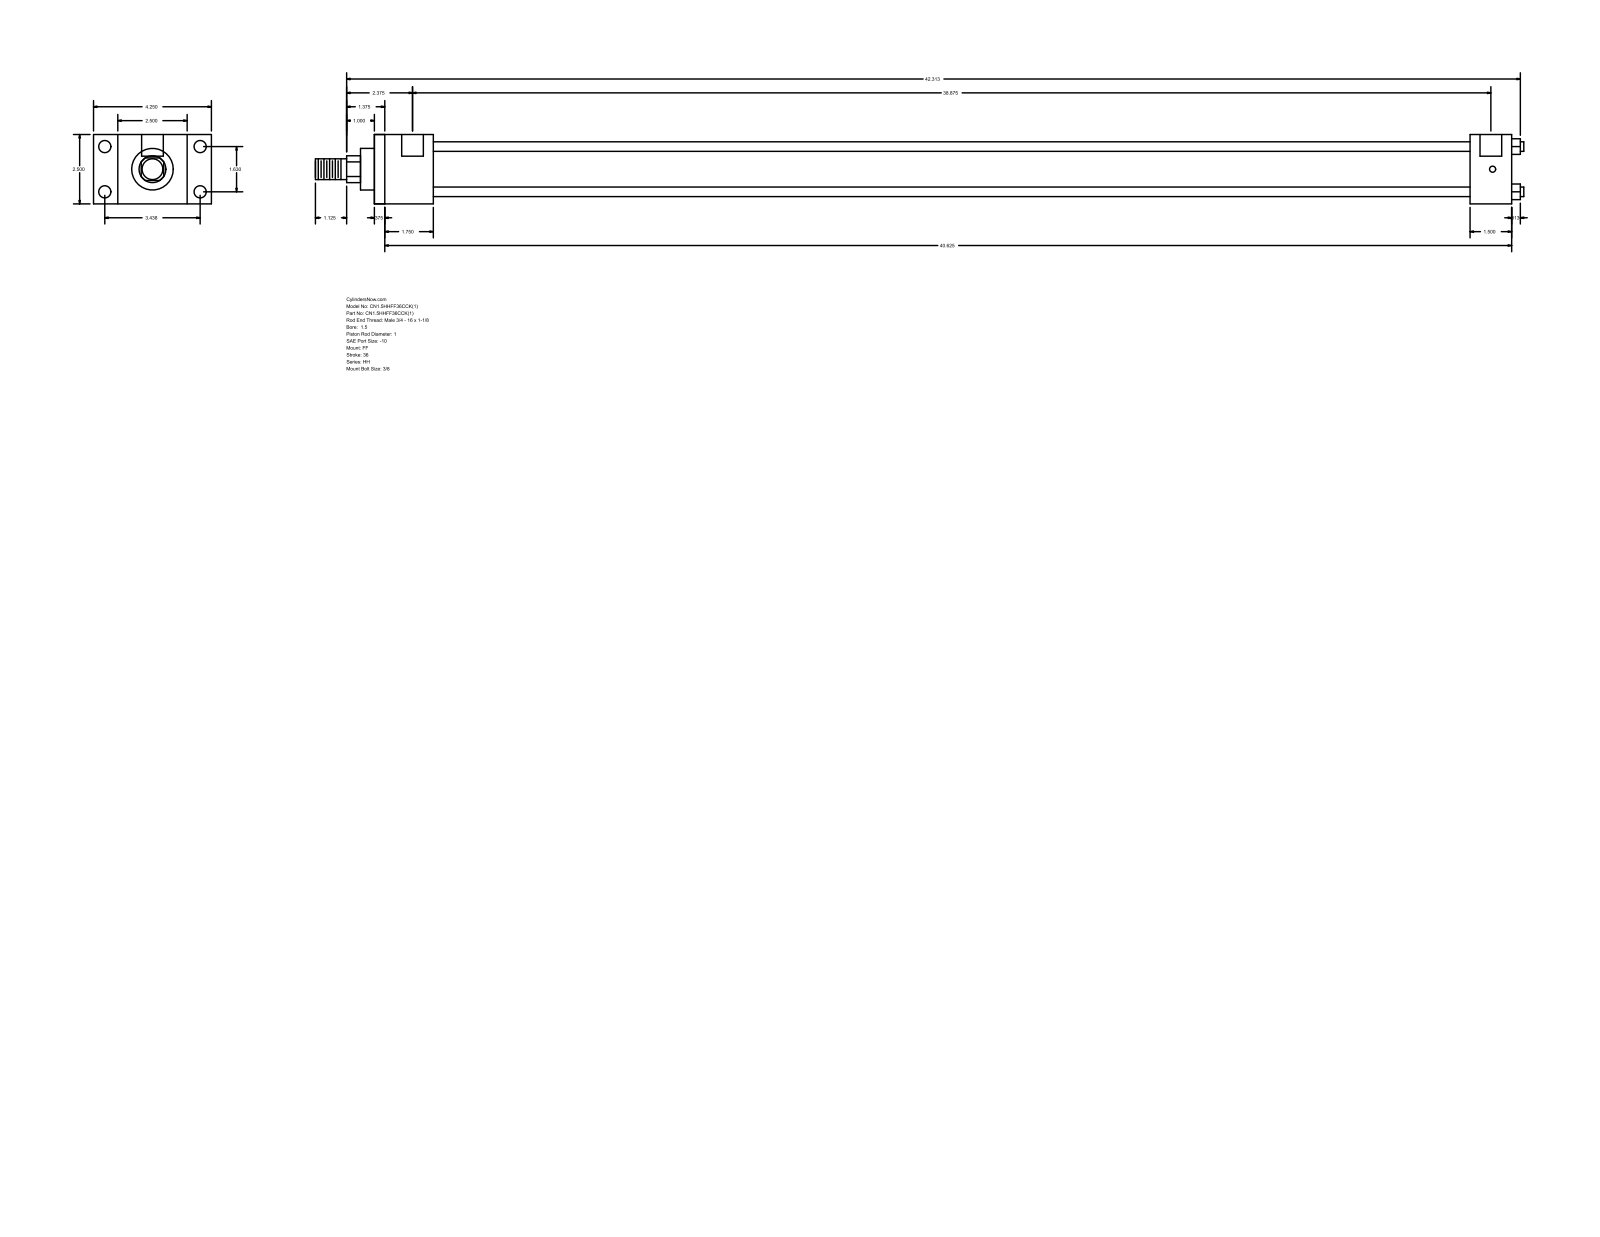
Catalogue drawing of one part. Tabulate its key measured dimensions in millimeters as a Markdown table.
| quantity | value |
| --- | --- |
| part name | HH_FF__0150_1 |
| STEP written by | GSSL Pune (CONFIG_CONTROL_DESIGN) |
| units | millimeters |
| bodies | 0 solids, 92 faces (64 planar, 28 cylindrical, 0 other) |
| overall size | 1106.49 × 107.95 × 63.5 |
| round holes (diameter × count) | 5.56 × 4, 11.13 × 4, 19.84 × 2 |
| round bosses / shafts (diameter × count) | 8.76 × 4, 44.45 × 1, 38.1 × 1, 25.4 × 1, 19.05 × 1 |
| partial cylindrical surfaces (radius × count) | 12.29 × 1 |
| main face-to-face distances | 63.5, 1041.4, 9.52, 1031.88, 38.1, 53.98, 44.46, 987.42, 1003.3, 993.78 |
| hole center spacings | 1.59, 41.4, 87.32, 96.64, 989.01, 990.6, 987.42 |
